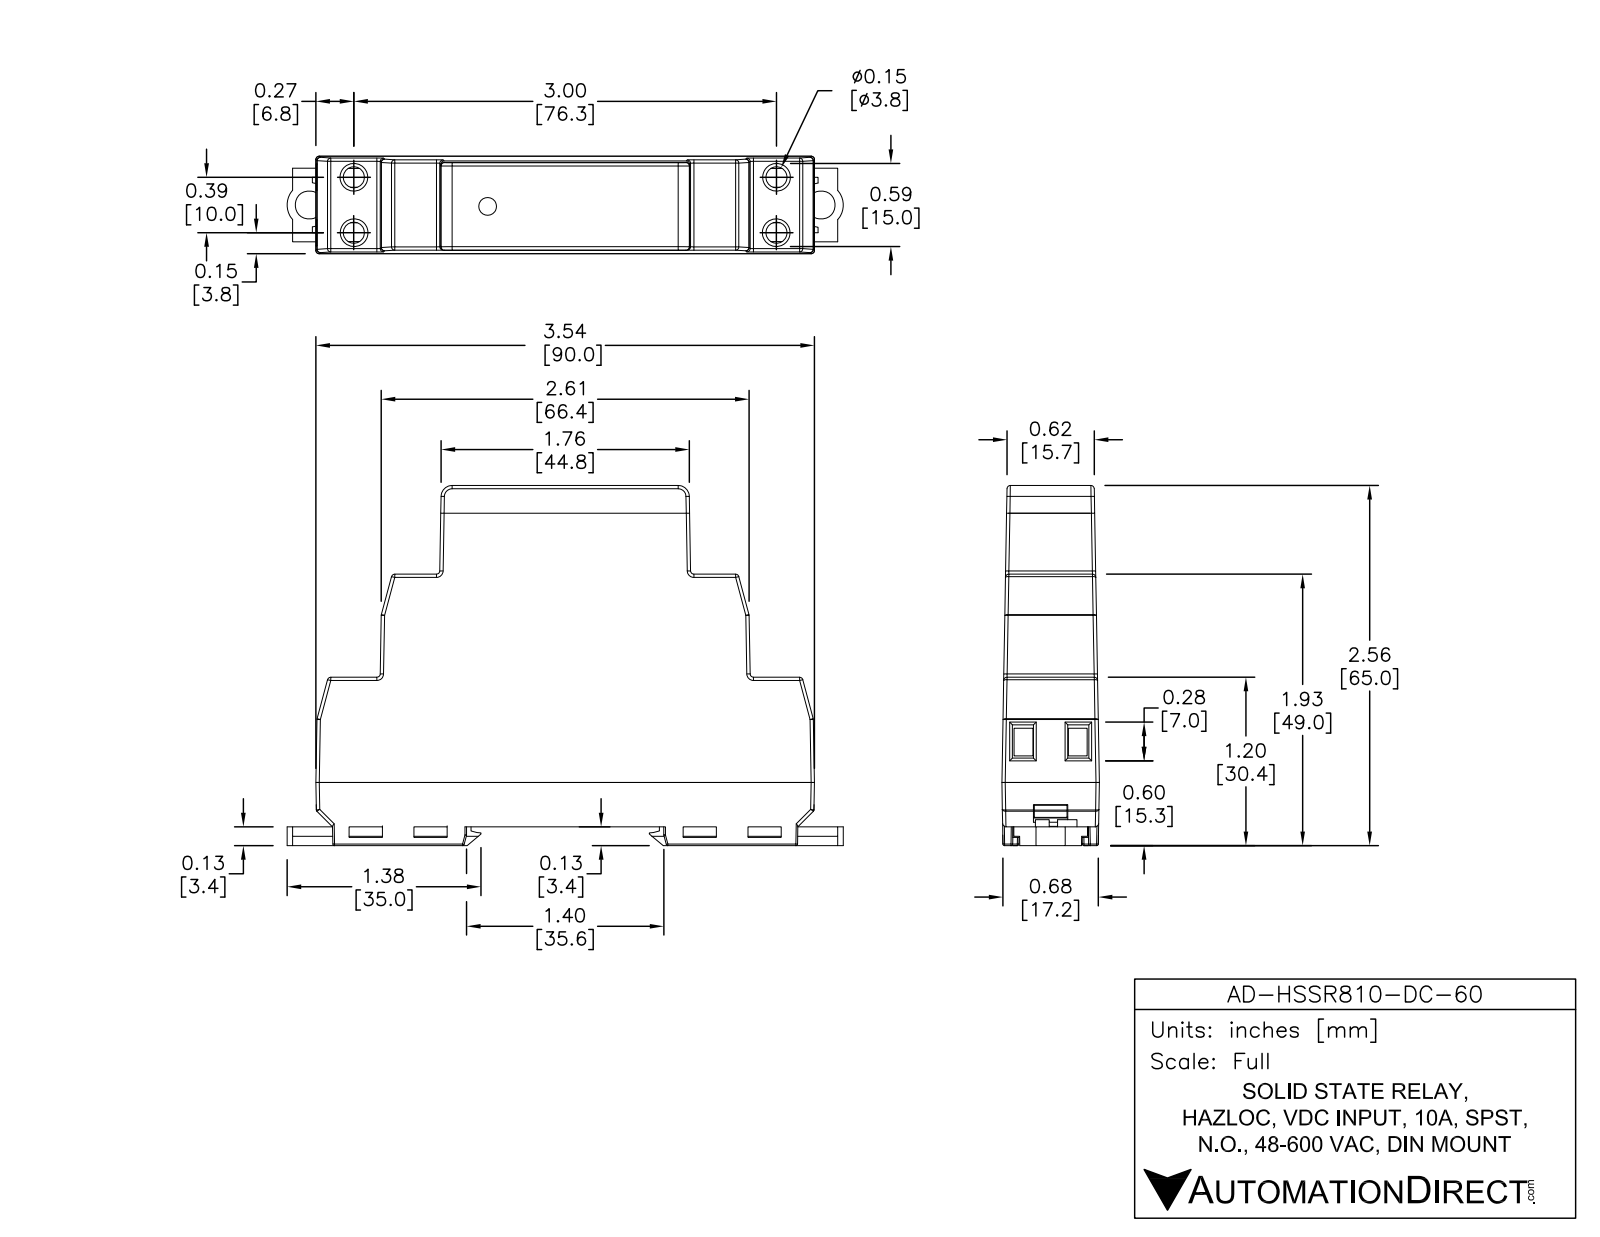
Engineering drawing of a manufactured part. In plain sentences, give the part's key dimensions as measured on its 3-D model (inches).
The part is named "AD-HSSR810-DC-60". Its 3-D file was written by "SolidWorks 2013 (AUTOMOTIVE_DESIGN)". It is 35 solids with 1264 faces: 673 planar, 65 cylindrical and 526 other. Overall it measures 3.952 by 2.619 by 0.692 inches. Its volume is 4.725 cubic inches and its surface area 25.56 square inches. Round holes: 4 of diameter 0.2, 2 of diameter 0.19. Round bosses or shafts: 4 of diameter 0.175, 1 of diameter 0.1. Partial cylindrical surfaces (rounded edges, fillets, slot ends): 10 of radius 0.02, 10 of radius 0.024, 6 of radius 0.012, 2 of radius 0.079, 2 of radius 0.15, 2 of radius 45.93. The main face-to-face distances are 0.136, 2.559, 2.423, 0.134, 2.425, 1.929, 1.795, 1.793, 0.63, 1.197. The hole center spacings are 3.335, 0.379, 0.38, 0.4, 3.006, 3.033, 3.652.
